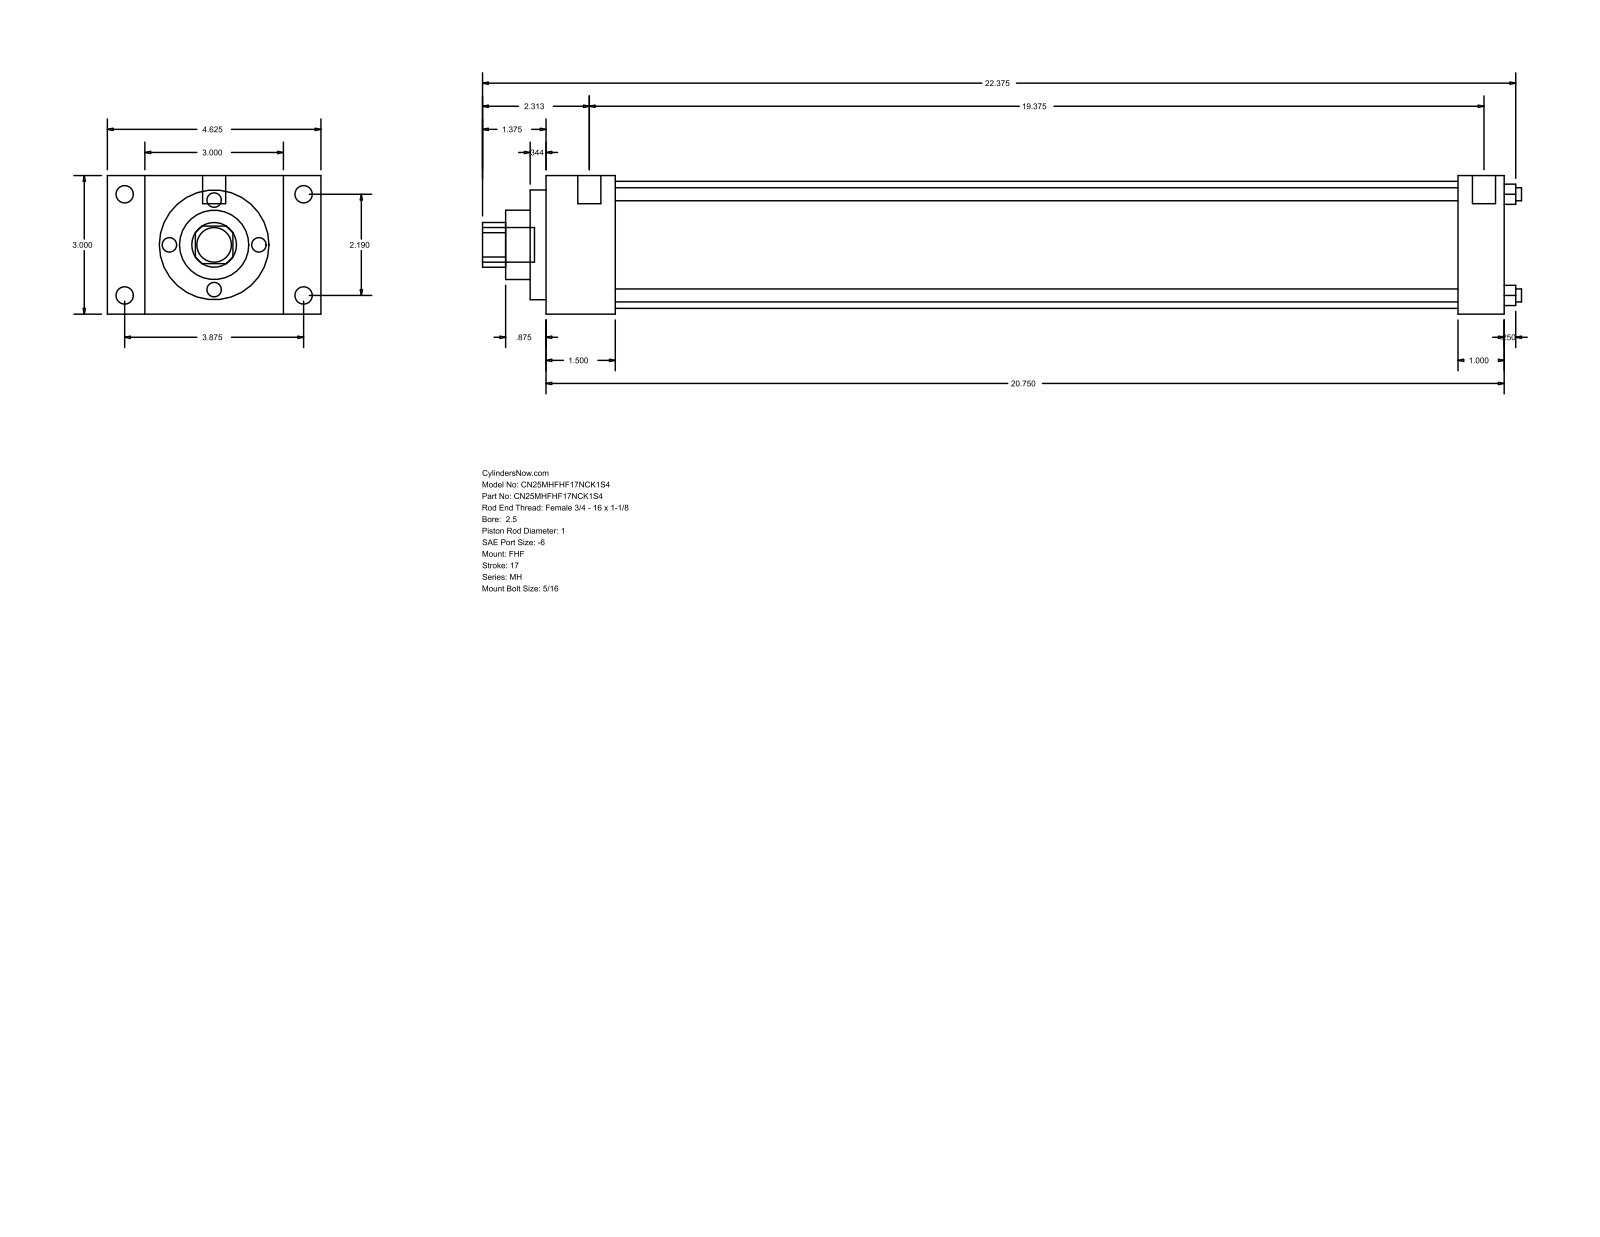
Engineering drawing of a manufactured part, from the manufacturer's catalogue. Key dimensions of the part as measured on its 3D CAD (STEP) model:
Part name (STEP PRODUCT): MH_FHF__0250_1
STEP written by: GSSL Pune (CONFIG_CONTROL_DESIGN)
Units: millimetres
Bodies: 0 solids, 90 faces (61 planar, 29 cylindrical, 0 other)
Overall size (bounding box): 571.5 × 117.47 × 76.2
Round holes (diameter × count): ⌀7.14 ×4, ⌀25.4 ×1, ⌀38.1 ×1, ⌀60.33 ×1, ⌀69.85 ×1
Round bosses / shafts (diameter × count): ⌀9.53 ×4, ⌀5.56 ×4, ⌀12.7 ×2, ⌀19.05 ×1
Partial cylindrical surfaces — rounded edges, fillets, slot ends (radius × count): R12.29 ×1
Main face-to-face distances: 76.2, 527.06, 38.11, 488.95, 20.64, 96.84, 117.48, 501.66, 463.55, 25.4
Hole centre spacings: 39.33, 55.62, 78.66
